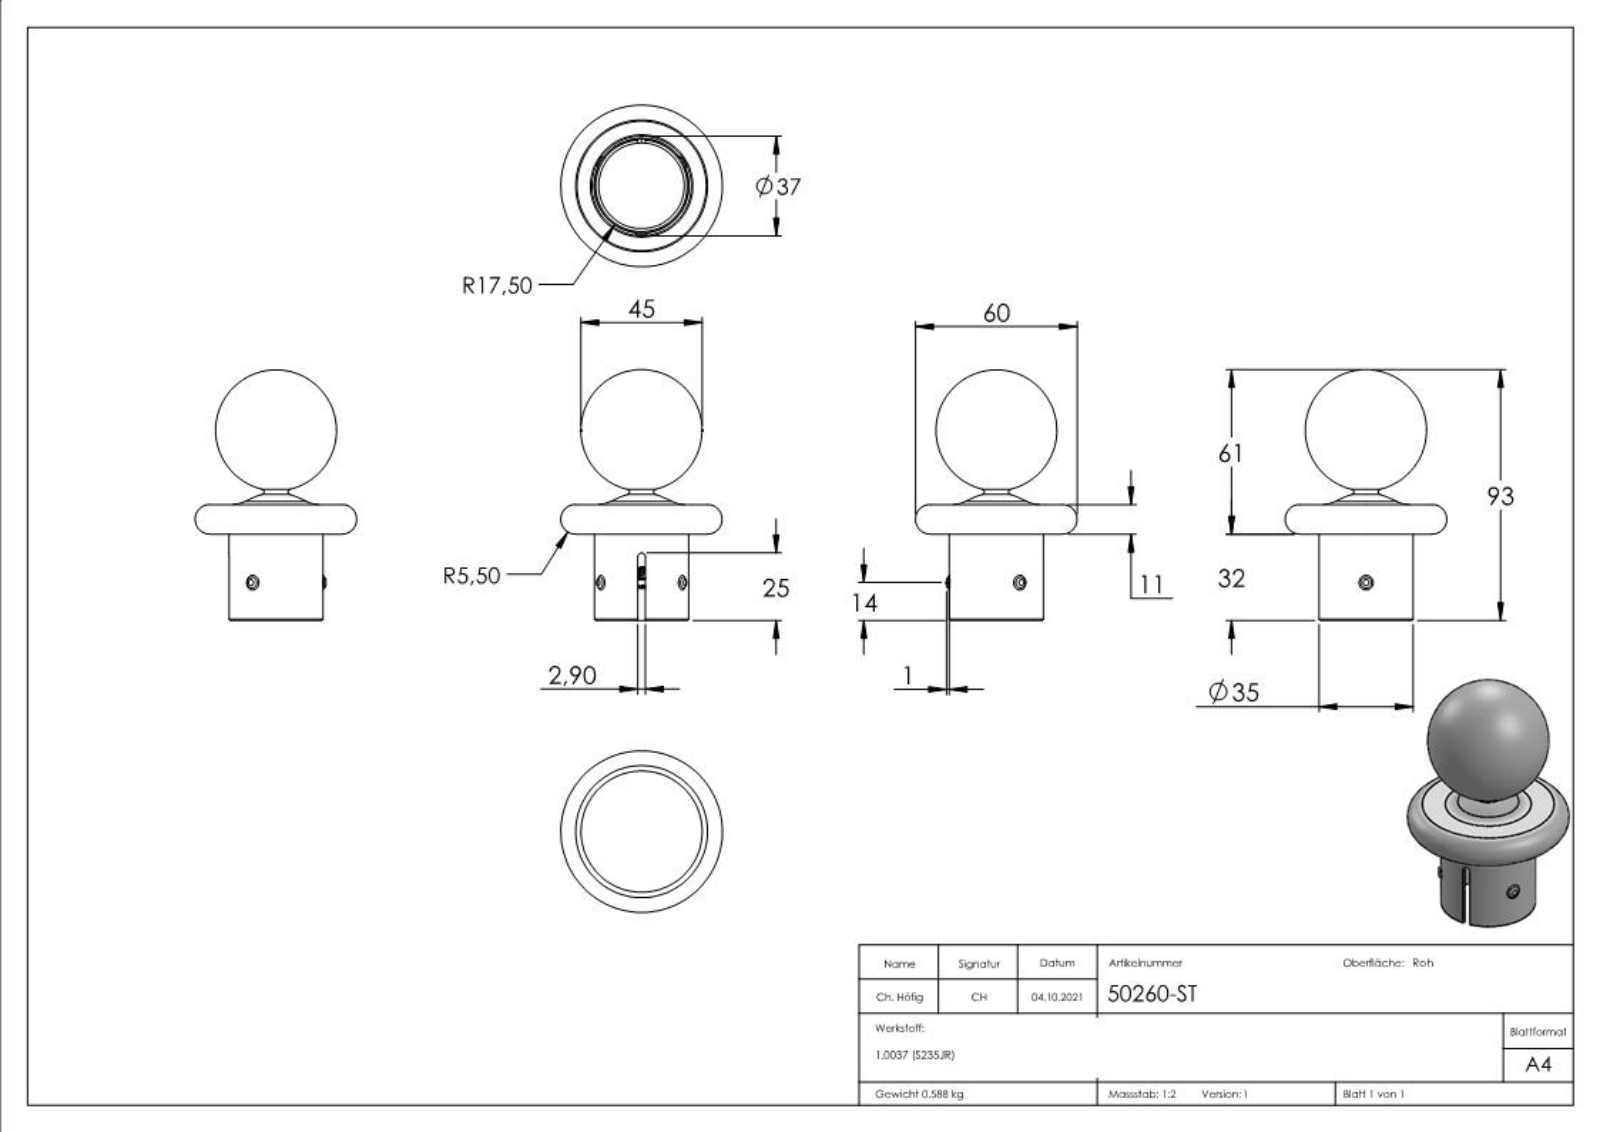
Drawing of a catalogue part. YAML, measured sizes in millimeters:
part_name: "50260-ST"
step_written_by: "SolidWorks 2018 (CONFIG_CONTROL_DESIGN)"
units: millimeters
bodies: {solids: 1, faces: 284, planar: 114, cylindrical: 31, other: 139}
overall_size: [93, 60, 60]
volume: 75409
surface_area: 21169
round_holes:
  - {diameter: 31.8, count: 1}
round_bosses_or_shafts:
  - {diameter: 35, count: 1}
partial_cylinders:
  - {radius: 1.45, count: 1}
  - {radius: 16, count: 1}
face_to_face_distances: [6, 37, 43, 32, 5, 11, 2.9, 2.7, 2.02, 2.46]
